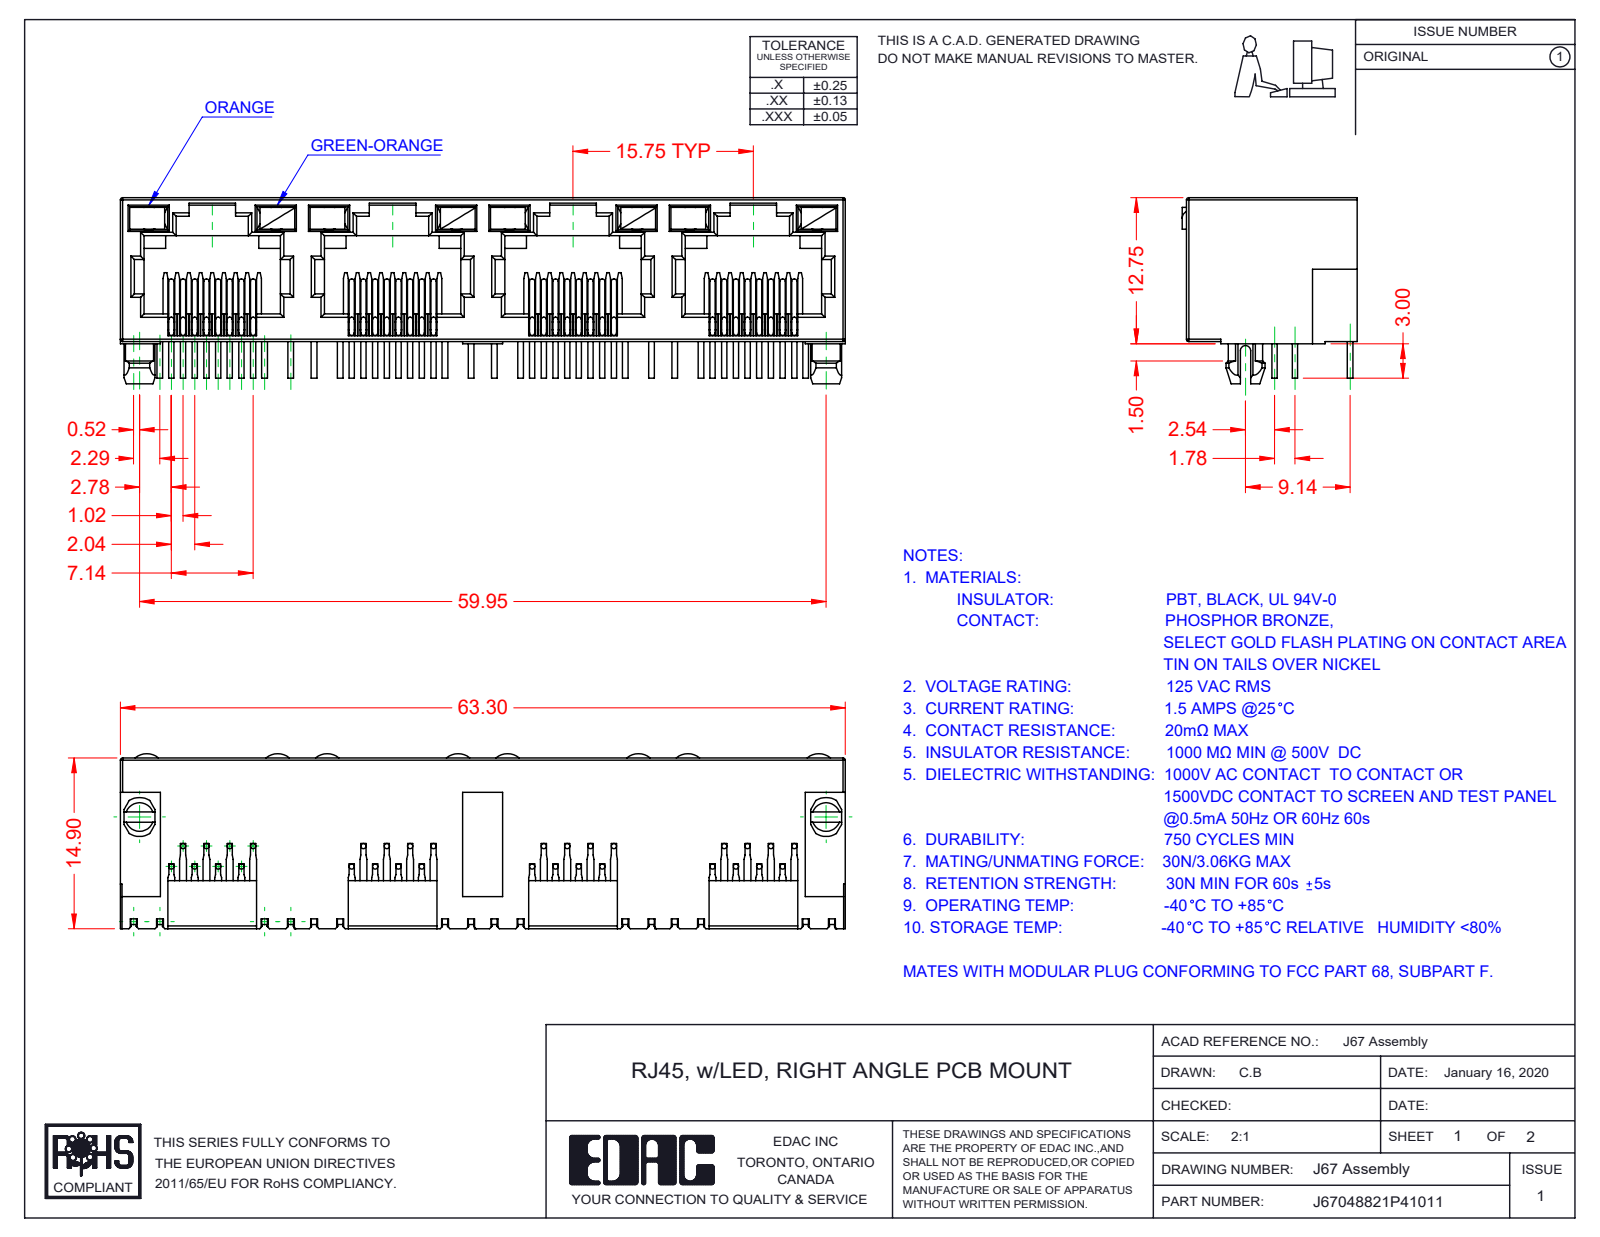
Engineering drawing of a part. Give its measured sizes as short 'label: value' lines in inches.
name: J67048822P47011; 67 Insulator; 67 LED RH_7-Green-Orange; 67 LED LH_4-Orange (+1 more)
written by: SolidWorks 2016 (CONFIG_CONTROL_DESIGN)
unit: in
bodies: 41 solids, 2473 faces (1781 planar, 484 cylindrical, 208 other)
size: 2.492 × 0.64 × 0.602
volume: 0.315 in³; area: 17.94 in²
bosses: 96× ⌀0.018
rounds: 66× R0.008, 29× R0.012, 9× R0.018, 8× R0.061, 2× R0.059, 2× R0.067, 1× R0.014, 1× R0.039
face distances: 0.02, 0.494, 0.074, 0.035, 0.394, 0.62, 0.039, 0.055, 0.433, 0.468
